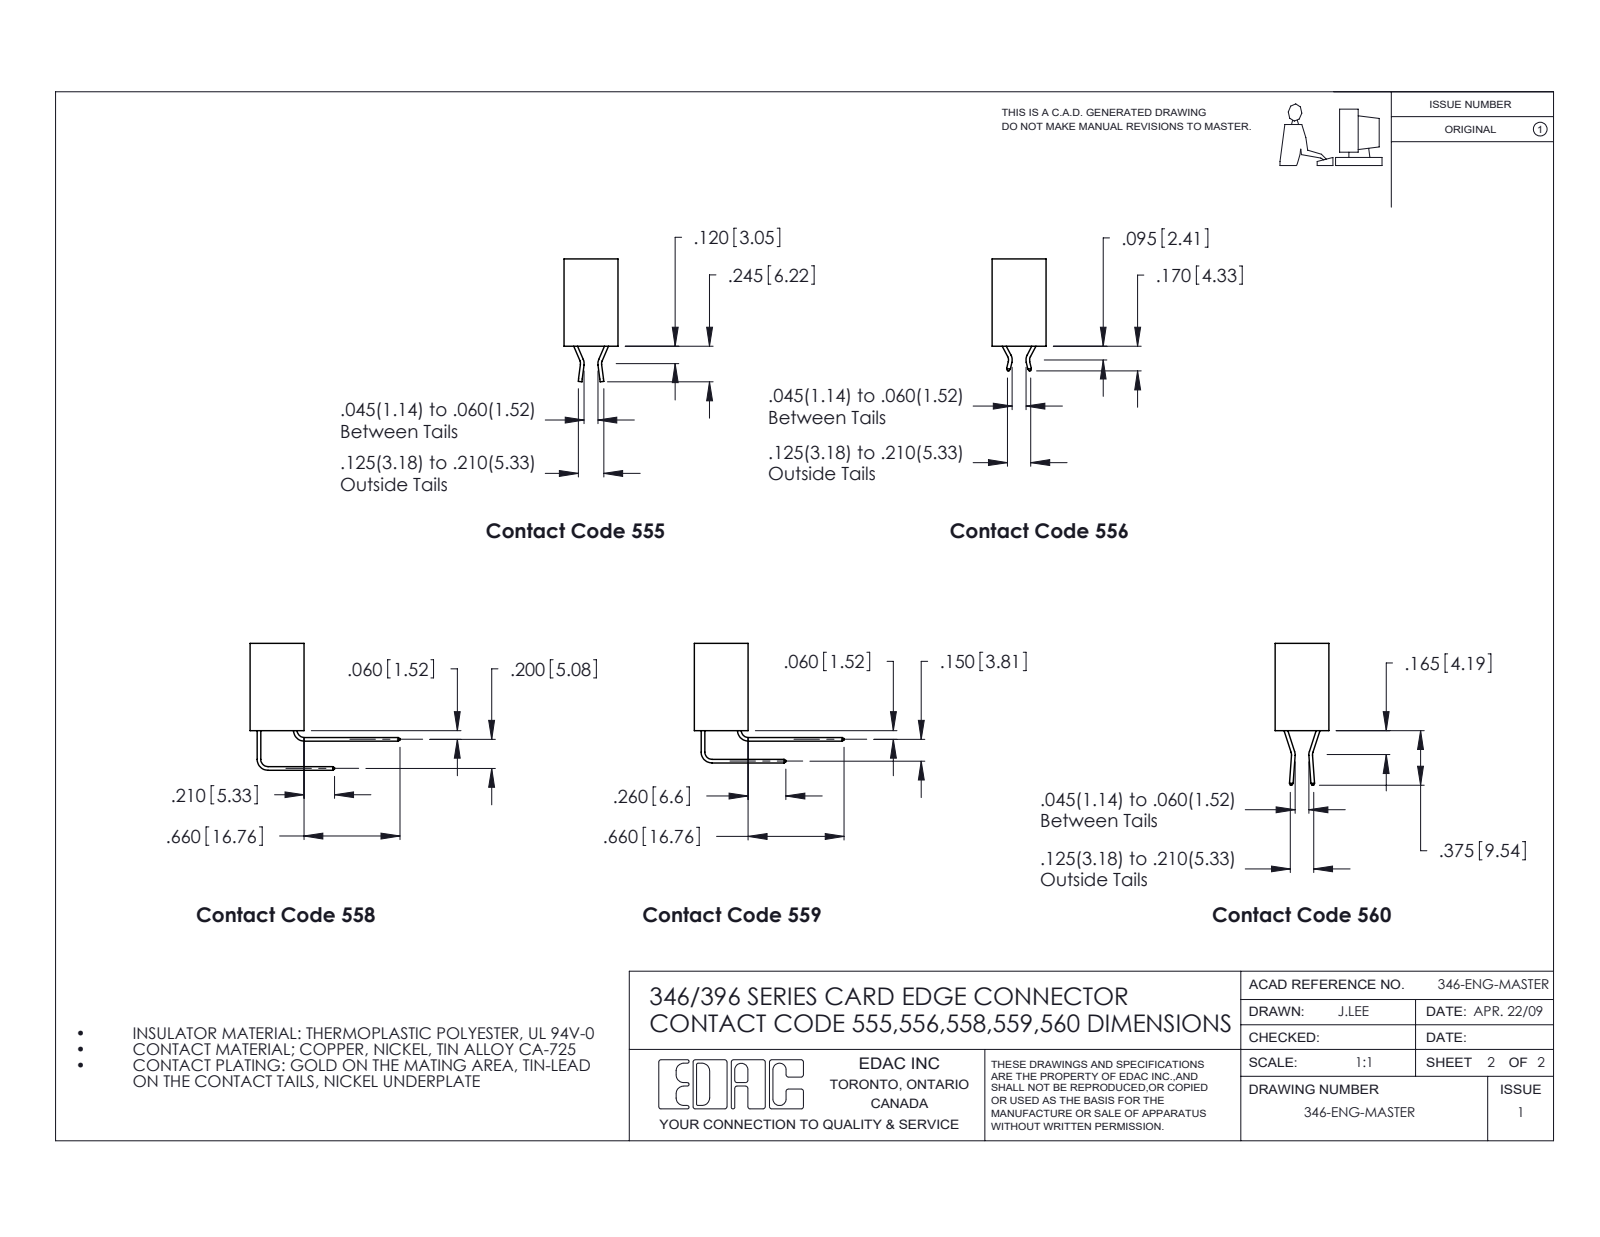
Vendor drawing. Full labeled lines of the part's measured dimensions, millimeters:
Part name (STEP PRODUCT): 346 Part_0.170 Offset - 0.128 Dia; 345-292-001_345-293-126; 346-012-526-802
STEP written by: SolidWorks 2020 (CONFIG_CONTROL_DESIGN)
Units: millimetres
Bodies: 13 solids, 738 faces (490 planar, 248 cylindrical, 0 other)
Overall size (bounding box): 36.4 × 24.1 × 9.4
Volume: 3 110 mm³ · Surface area: 3 800 mm²
Round holes (diameter × count): ⌀3.3 ×2, ⌀1.6 ×1
Partial cylindrical surfaces — rounded edges, fillets, slot ends (radius × count): R0.3 ×22, R0.2 ×18, R0.3 ×12, R0.2 ×6, R0.8 ×6, R0.7 ×3, R0.4 ×2, R0.6 ×2
Main face-to-face distances: 6.4, 9.4, 1.2, 8.2, 0.6, 1.8, 7.6, 7, 5.7, 3.8
Hole centre spacings: 6.2, 24.6, 29.7
